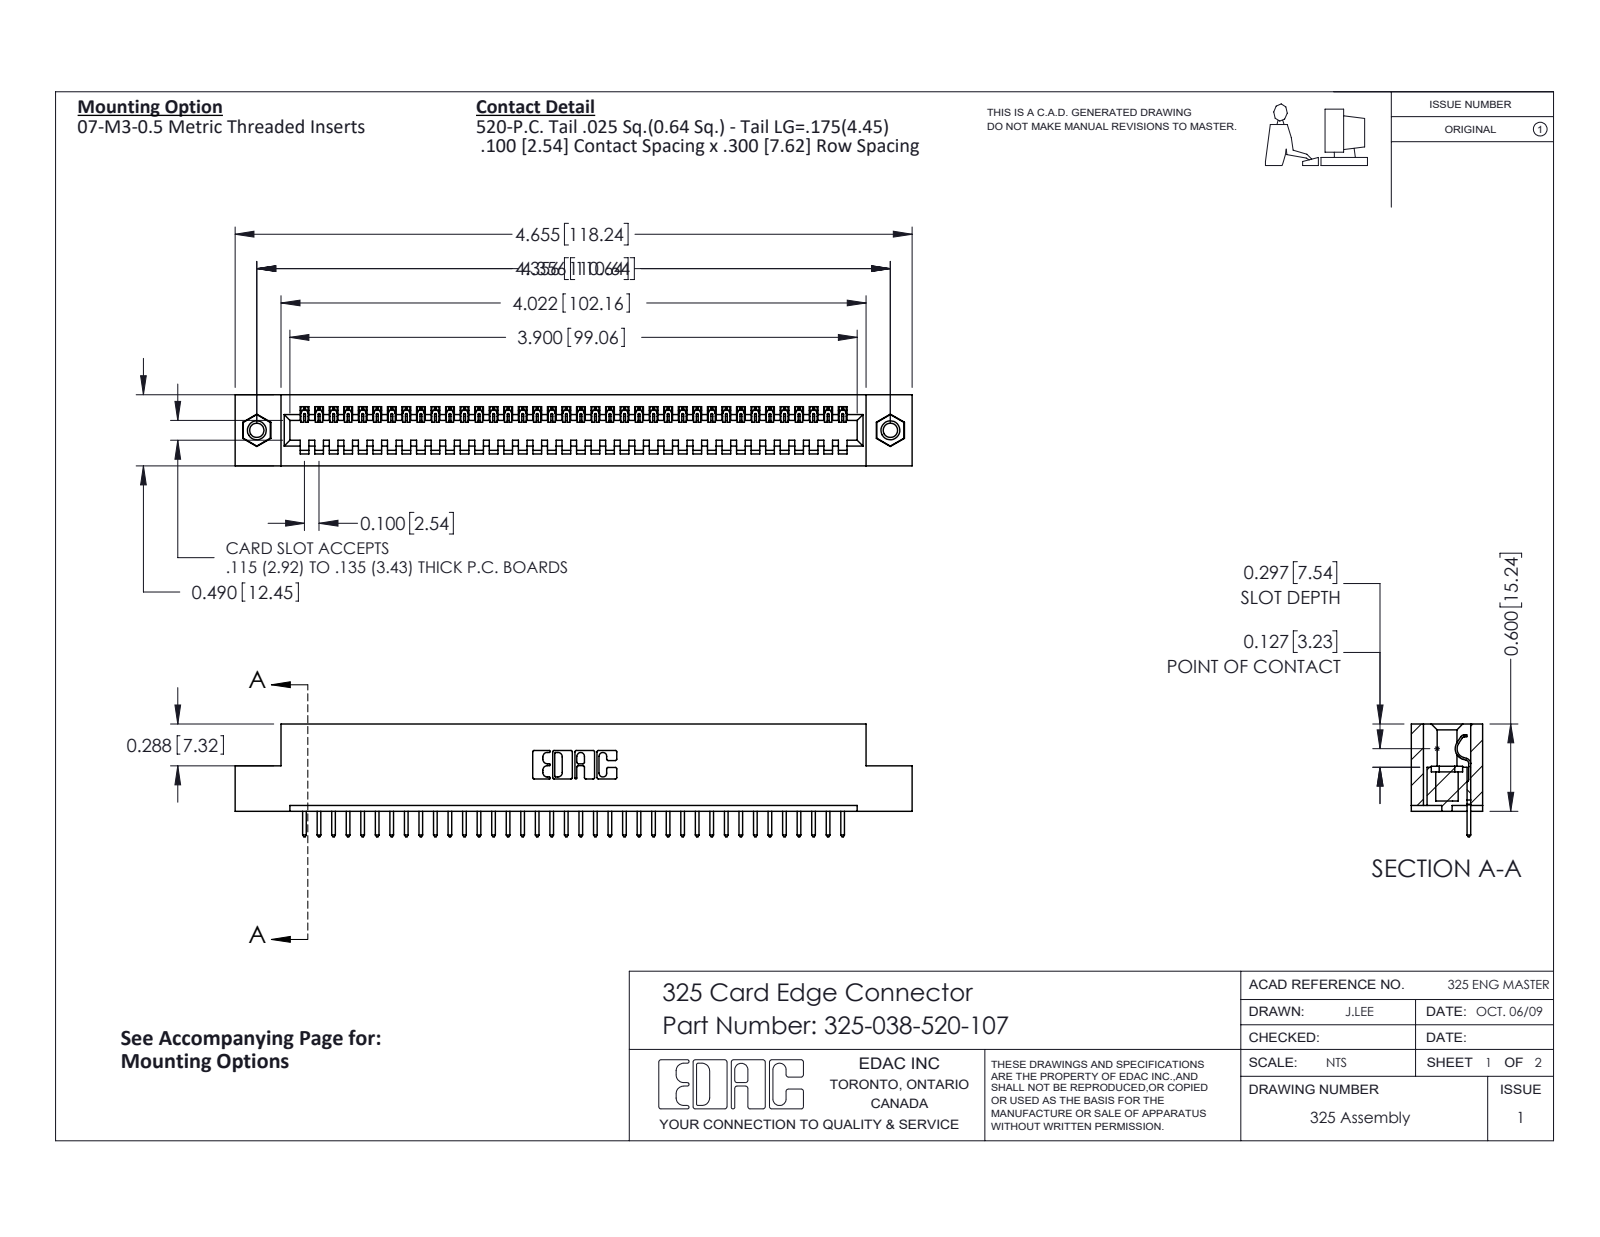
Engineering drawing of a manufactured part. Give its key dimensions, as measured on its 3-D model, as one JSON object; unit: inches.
{"part_name": "345-250-001_345-250-005-103; 325-038-520-107; 325-292-001_325-293-120; 325 Part_TI", "step_written_by": "SolidWorks 2016 (CONFIG_CONTROL_DESIGN)", "units": "inches", "bodies": {"solids": 41, "faces": 2378, "planar": 1698, "cylindrical": 664, "other": 16}, "overall_size": [4.655, 0.775, 0.49], "volume_in3": 0.907, "surface_area_in2": 24.49, "round_holes": [[0.098, 2], [0.125, 2], [0.16, 2]], "round_bosses_or_shafts": [[0.155, 2]], "partial_cylinders_radius": [[0.006, 76], [0.01, 76], [0.01, 22], [0.007, 6], [0.031, 6], [0.026, 3], [0.014, 1], [0.022, 1]], "face_to_face_distances": [0.083, 0.407, 0.49, 0.3, 0.107, 0.383, 0.025, 0.325, 0.56, 0.263], "hole_center_spacings": [4.356]}
